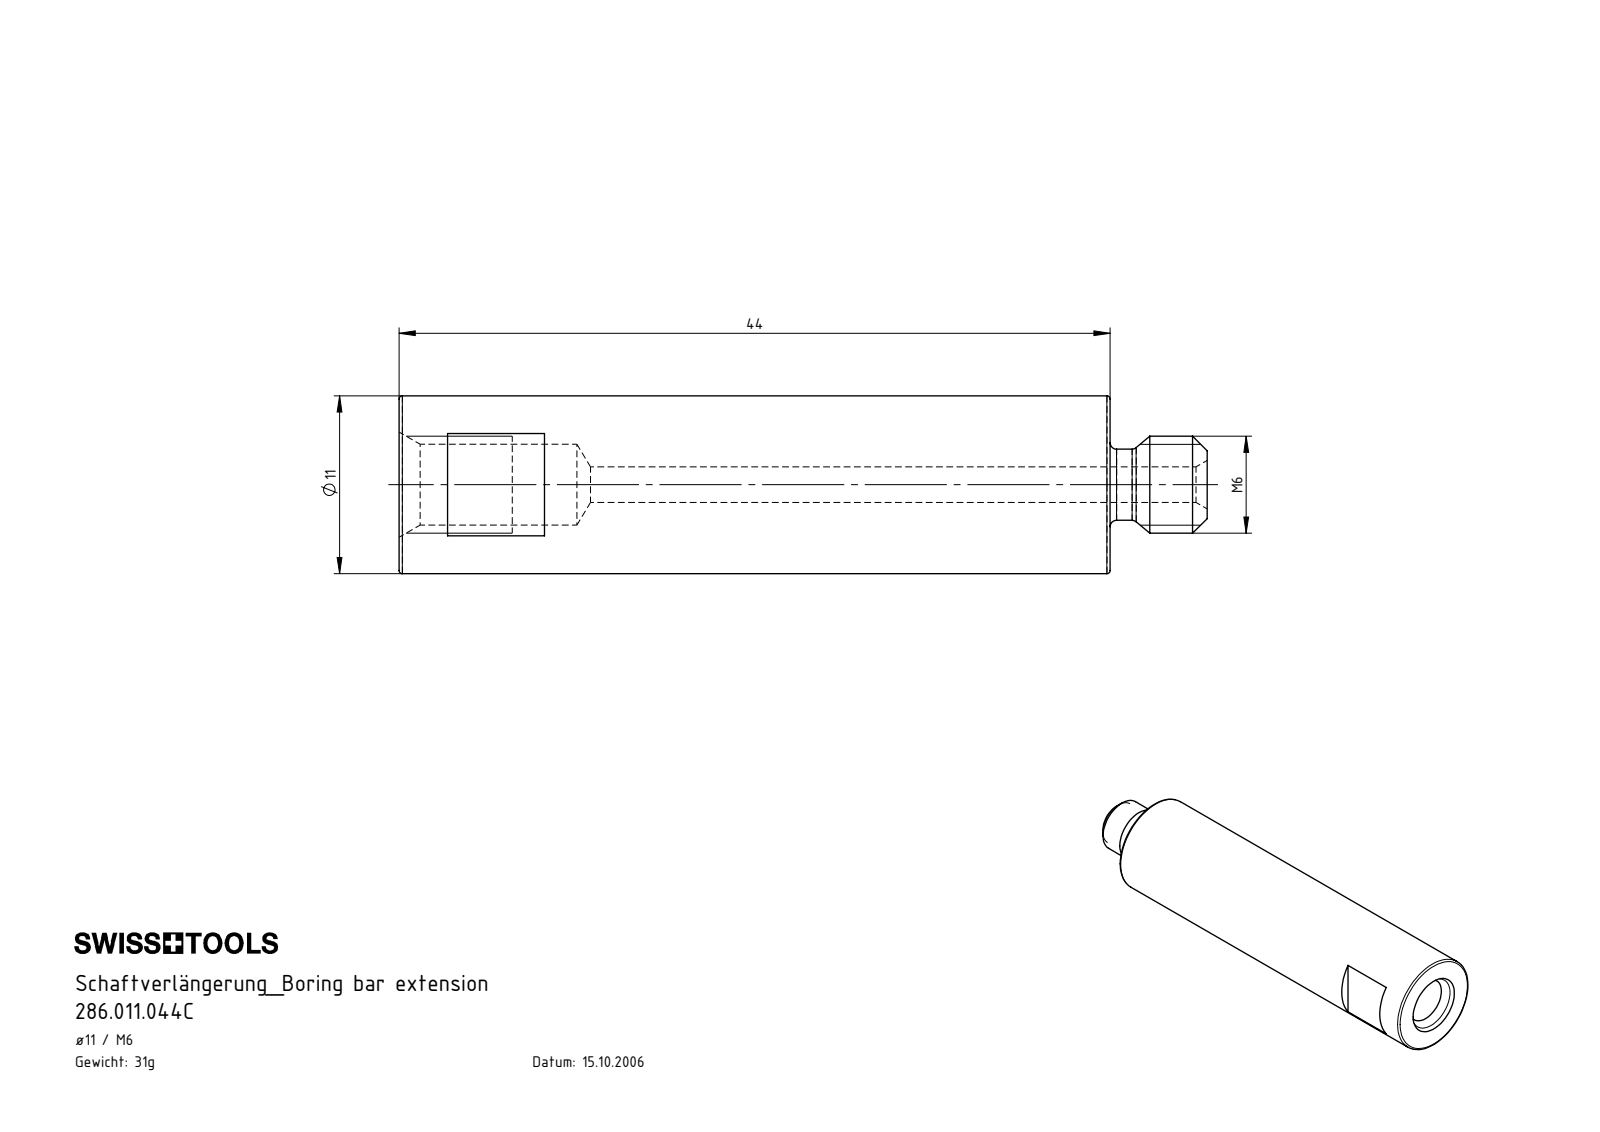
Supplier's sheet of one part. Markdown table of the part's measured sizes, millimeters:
| quantity | value |
| --- | --- |
| part name | 286.011.044C |
| STEP written by | SolidWorks 2022 (CONFIG_CONTROL_DESIGN) |
| units | millimeters |
| bodies | 1 solid, 37 faces (9 planar, 10 cylindrical, 18 other) |
| overall size | 50 × 11 × 11 |
| volume | 3 887 mm³ |
| surface area | 2 248 mm² |
| round holes (diameter × count) | 2.2 × 1, 5 × 1 |
| round bosses / shafts (diameter × count) | 11 × 1, 6 × 1, 4.4 × 1 |
| main face-to-face distances | 44, 9, 41, 6, 3, 35, 47, 50 |
